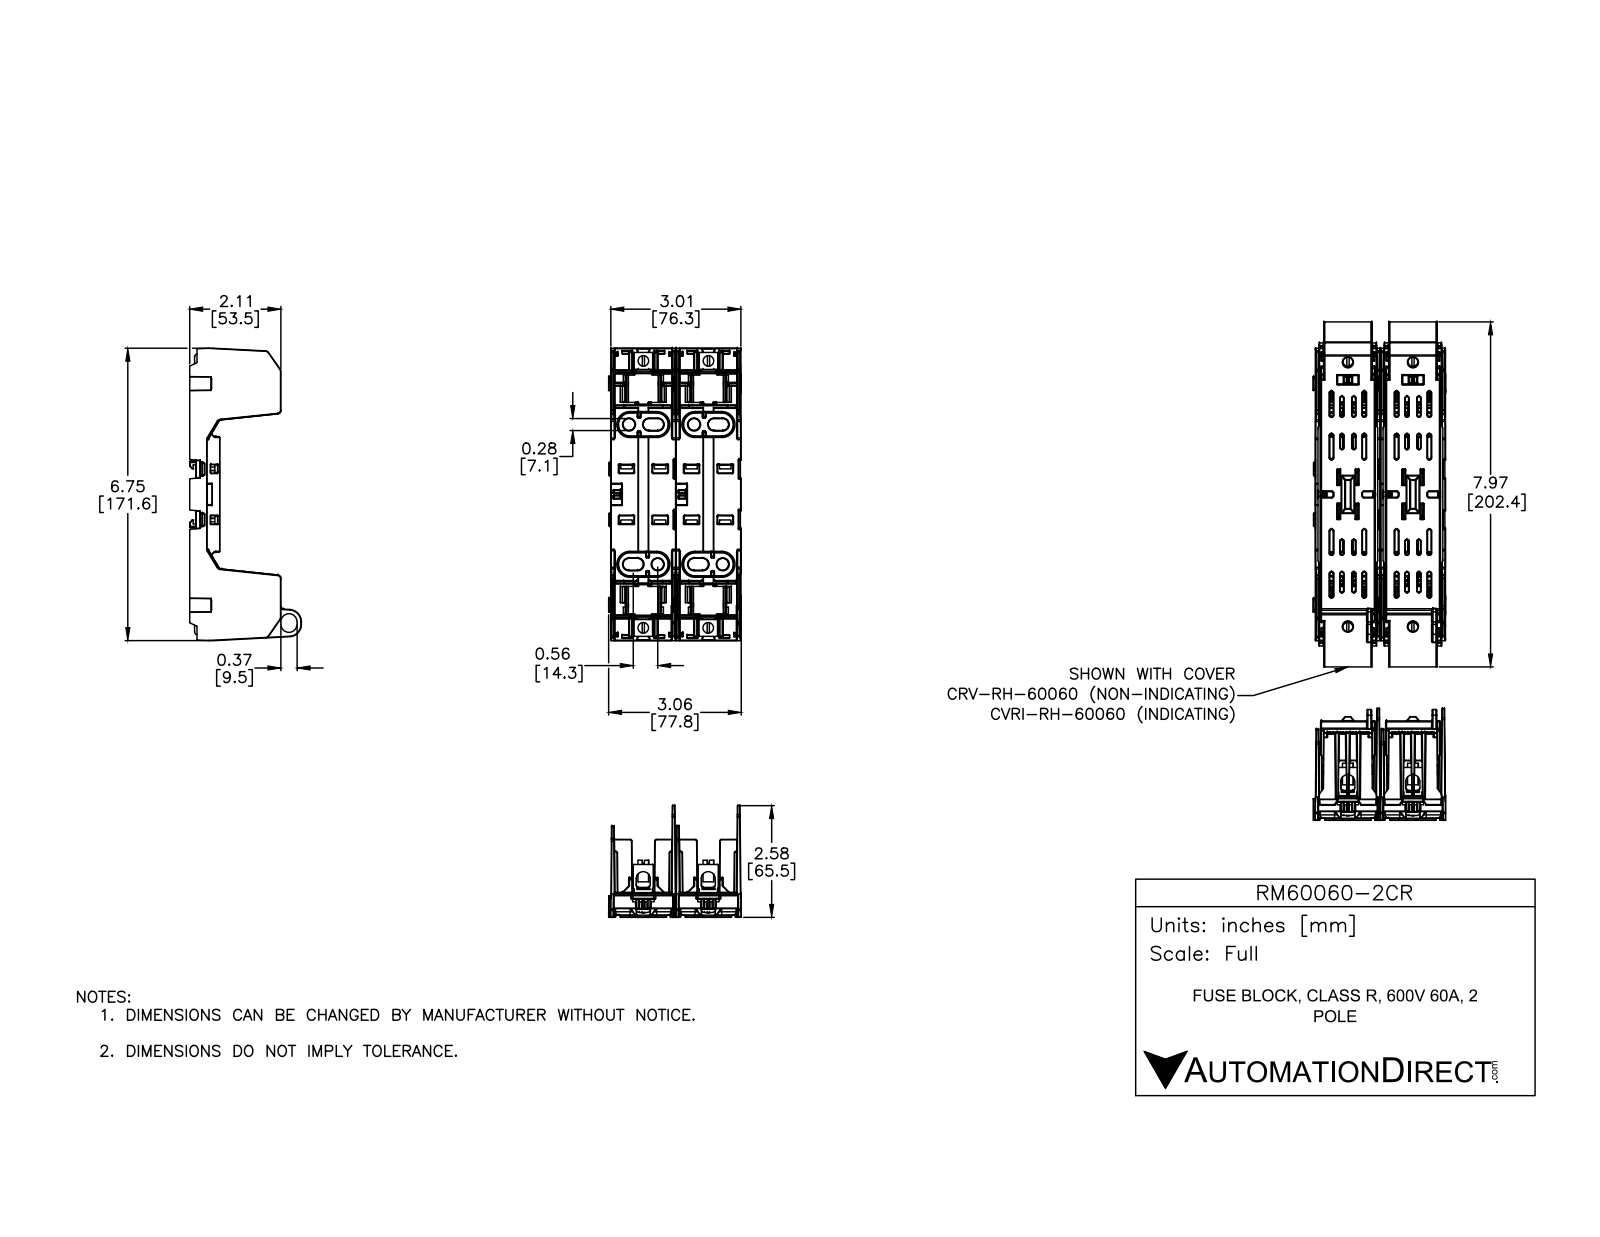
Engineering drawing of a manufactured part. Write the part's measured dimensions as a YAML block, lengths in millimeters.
part_name: "RM60060-2CR"
step_written_by: "SolidWorks 2021 (CONFIG_CONTROL_DESIGN)"
units: millimeters
bodies: {solids: 14, faces: 1594, planar: 934, cylindrical: 438, other: 222}
overall_size: [171.6, 77.8, 65.5]
volume: 168500
surface_area: 99350
round_holes:
  - {diameter: 6.2, count: 4}
  - {diameter: 7.1, count: 4}
round_bosses_or_shafts:
  - {diameter: 8.5, count: 4}
  - {diameter: 6.2, count: 4}
partial_cylinders:
  - {radius: 0.2, count: 70}
  - {radius: 0.3, count: 38}
  - {radius: 0.5, count: 32}
  - {radius: 1, count: 16}
  - {radius: 1.8, count: 8}
  - {radius: 2, count: 8}
  - {radius: 3.5, count: 8}
  - {radius: 7, count: 8}
face_to_face_distances: [38.2, 38.3, 76.5, 5.1, 14.5, 9.4, 2, 143.7, 3.4, 8.5]
hole_center_spacings: [38.2, 38.3, 119.6, 47.7, 59.7, 83.7, 123, 128.1]
